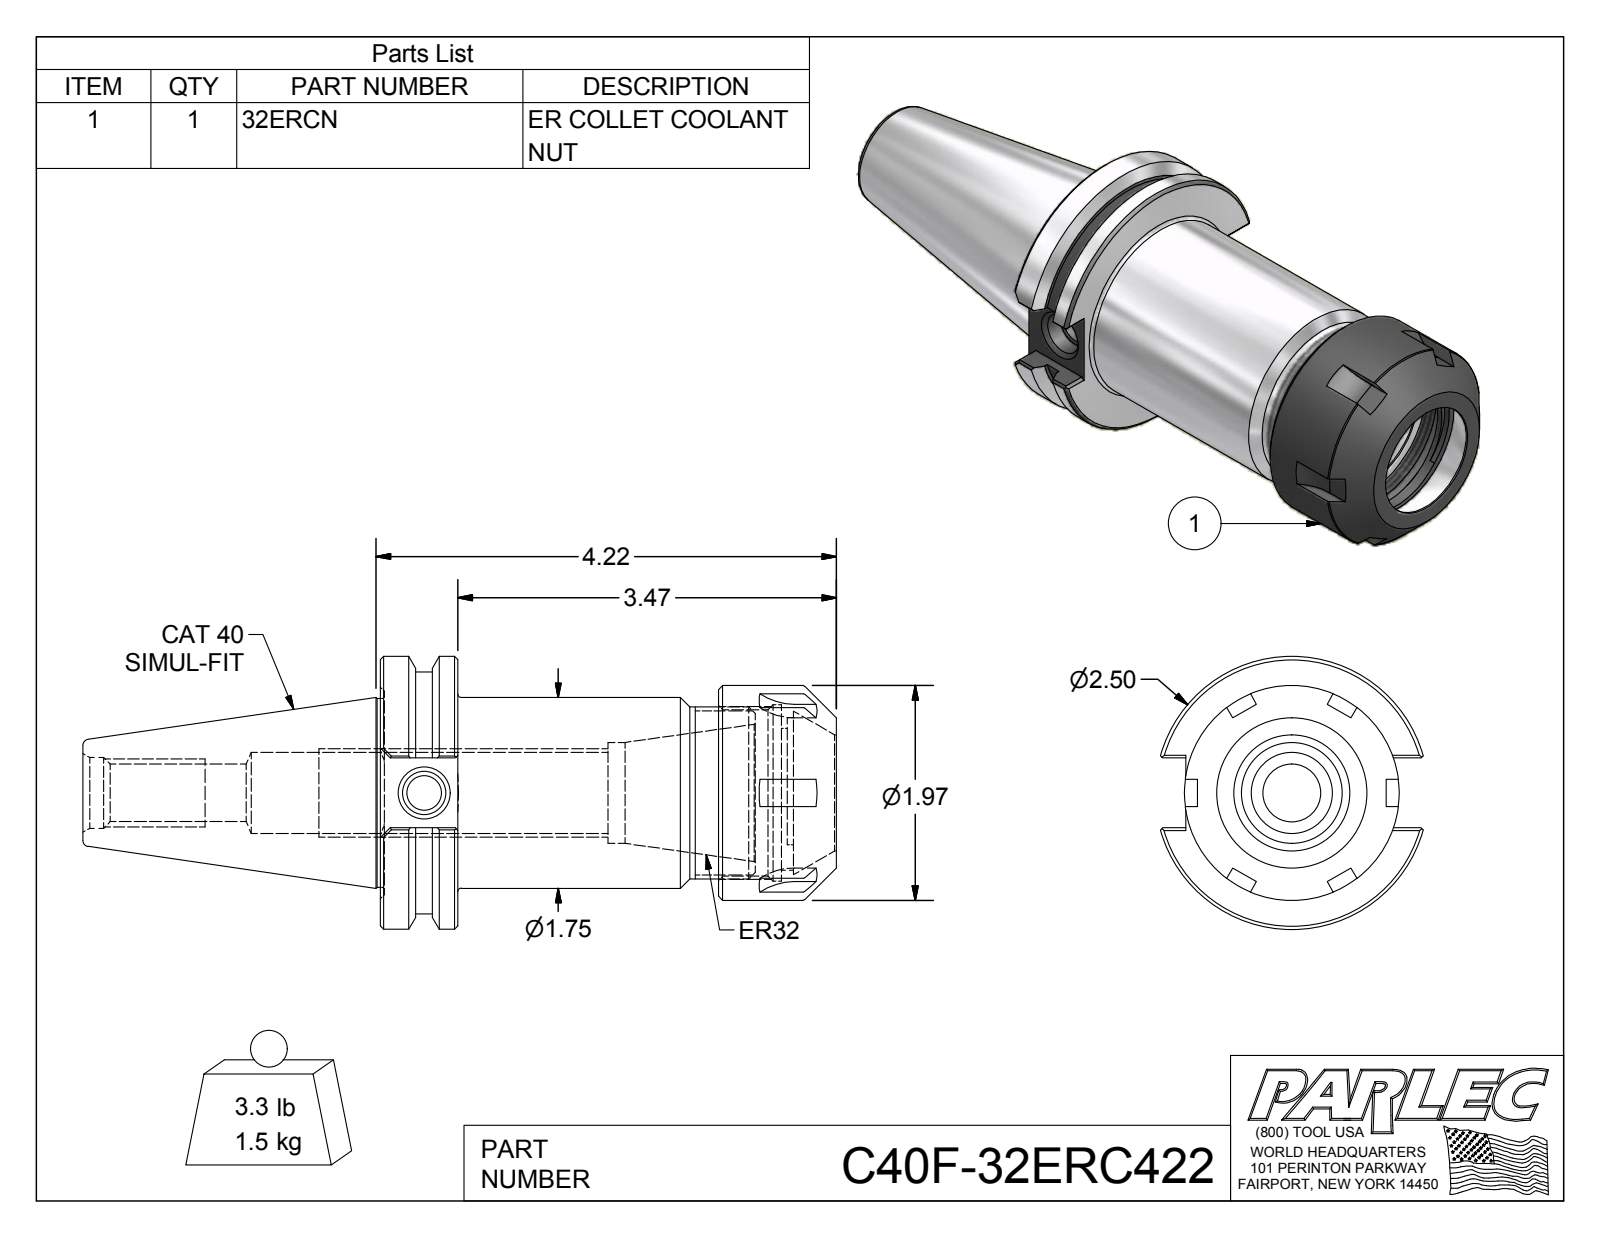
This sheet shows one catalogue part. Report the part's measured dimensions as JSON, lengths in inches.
{"part_name": "C40F-32ERC422; C40F-32ER4-1; 32ERCN", "step_written_by": "Autodesk Inventor 2012 (AUTOMOTIVE_DESIGN)", "units": "inches", "bodies": {"solids": 2, "faces": 121, "planar": 56, "cylindrical": 27, "other": 38}, "overall_size": [6.908, 2.5, 2.406], "volume_in3": 11.53, "surface_area_in2": 69.84, "round_holes": [[0.315, 1], [0.399, 1], [0.527, 1], [0.648, 1], [0.745, 1], [0.925, 1], [1.063, 1], [1.299, 1], [1.522, 1], [1.614, 1]], "round_bosses_or_shafts": [[2.5, 1], [2.215, 1], [1.969, 1], [1.75, 1], [1.73, 1], [1.575, 1]], "partial_cylinders_radius": [[0.5, 6], [0.689, 1]], "face_to_face_distances": [0.711, 3.098, 2.387, 3.677, 2.966, 0.579, 4.181, 3.47, 1.083, 0.504], "hole_center_spacings": [0.059]}
